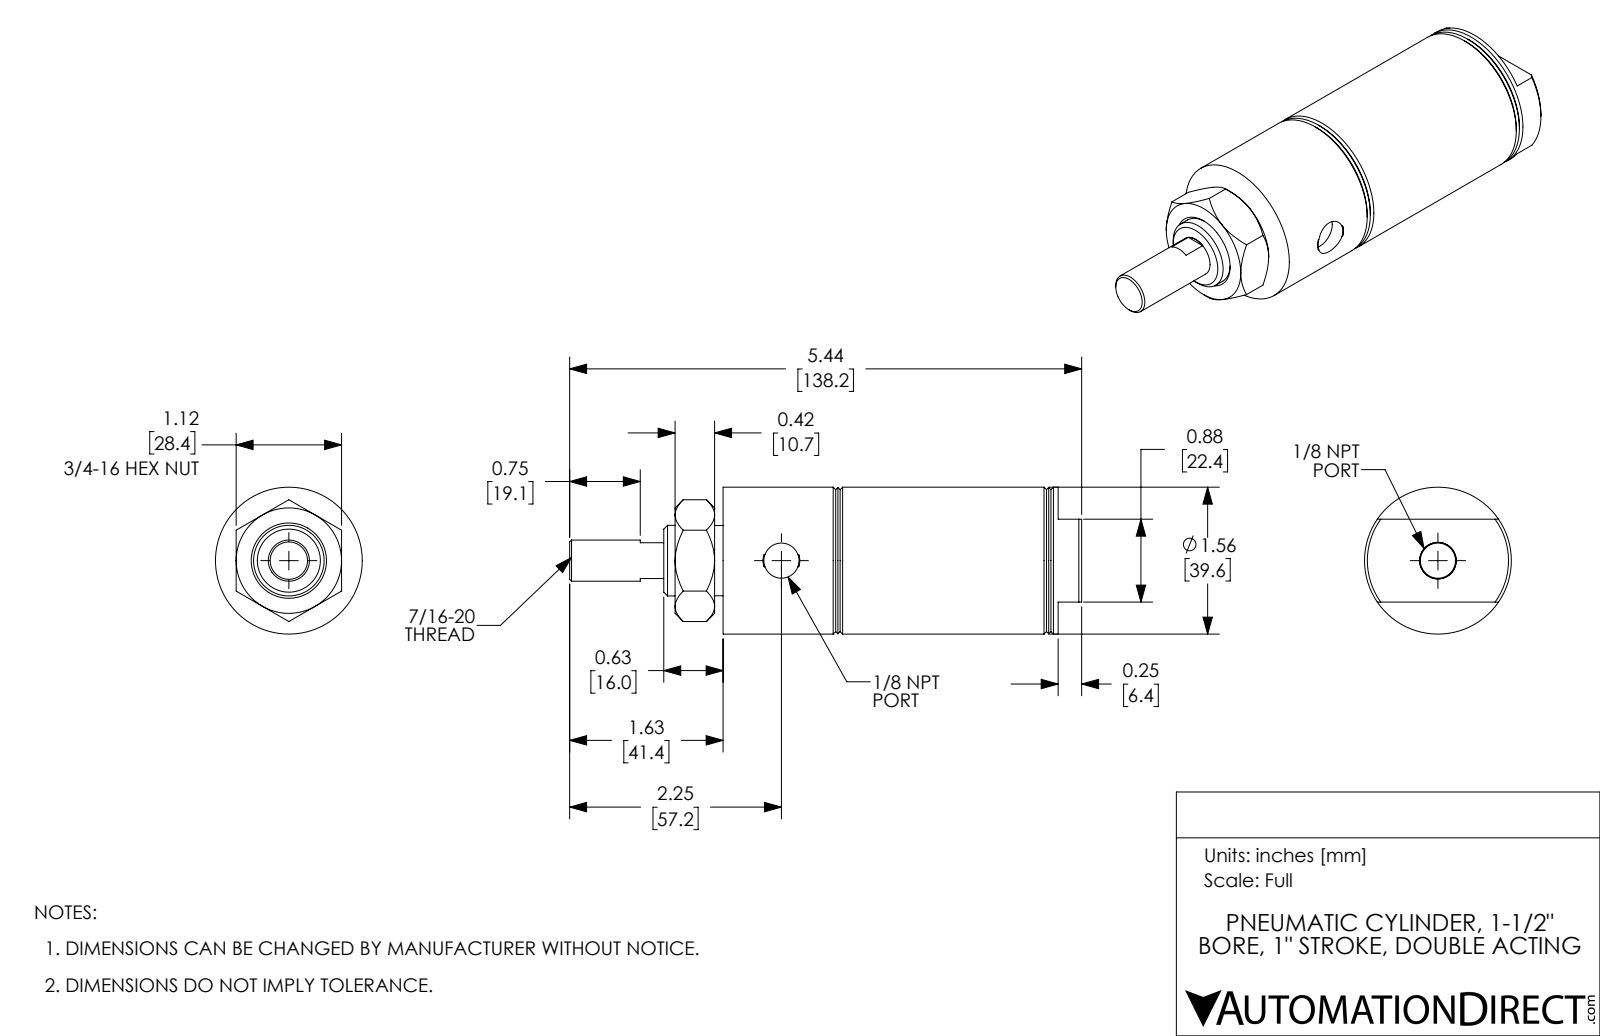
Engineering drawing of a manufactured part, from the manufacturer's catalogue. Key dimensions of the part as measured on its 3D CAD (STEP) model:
Part name (STEP PRODUCT): A24010DN_Mounting Nut_D-3556; A24010DN; A24010DN-Rod; A24010DN-MainBody
STEP written by: SolidWorks 2017 (AUTOMOTIVE_DESIGN)
Units: inches
Bodies: 3 solids, 104 faces (32 planar, 24 cylindrical, 48 other)
Overall size (bounding box): 5.44 × 1.56 × 1.56
Volume: 6.142 in³ · Surface area: 52.62 in²
Round holes (diameter × count): ⌀0.374 ×2, ⌀0.437 ×1, ⌀0.75 ×1, ⌀1.5 ×1
Round bosses / shafts (diameter × count): ⌀1.56 ×1, ⌀0.746 ×1
Main face-to-face distances: 1, 0.5, 1.5, 2.84, 2.34, 1.34, 0.97, 1.47, 2.47, 3.81
